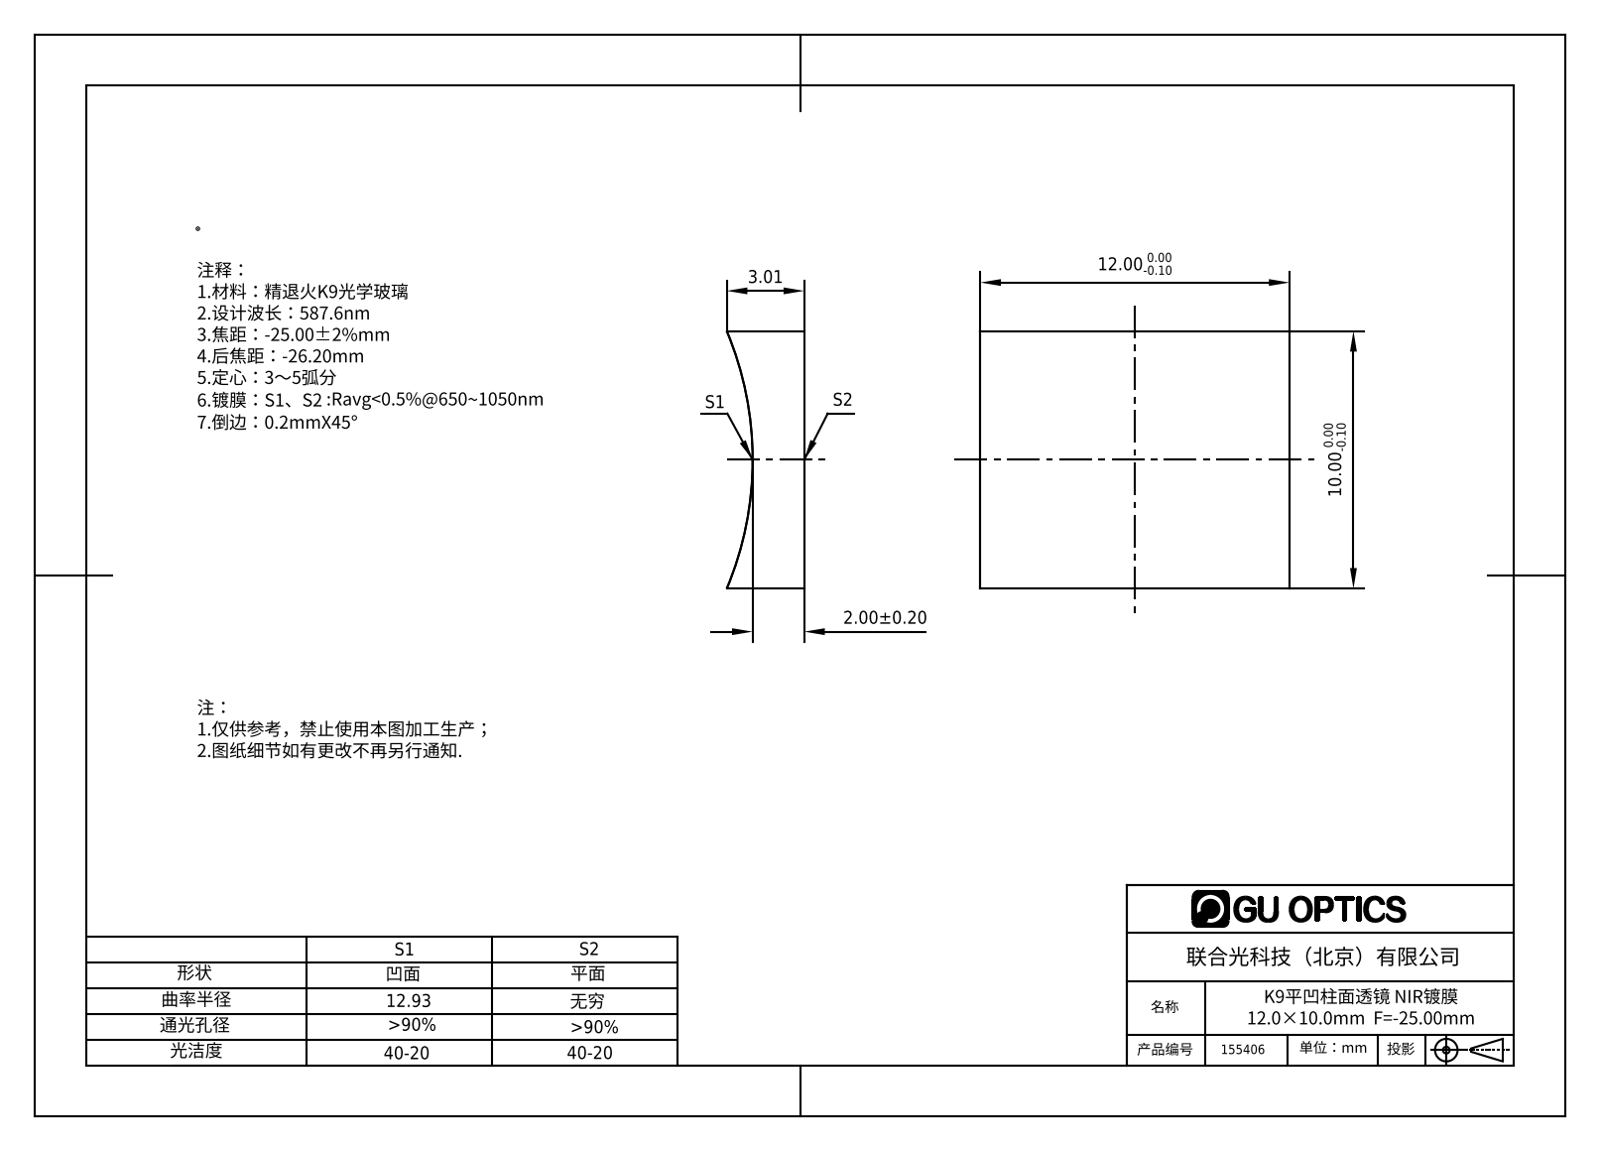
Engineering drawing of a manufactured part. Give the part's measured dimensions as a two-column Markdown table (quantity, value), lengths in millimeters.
| quantity | value |
| --- | --- |
| part name | 155340 |
| STEP written by | SolidWorks 2016 (AUTOMOTIVE_DESIGN) |
| units | millimeters |
| bodies | 1 solid, 6 faces (5 planar, 1 cylindrical, 0 other) |
| overall size | 12 × 10 × 3.01 |
| volume | 280 mm³ |
| surface area | 362 mm² |
| partial cylindrical surfaces (radius × count) | 12.93 × 1 |
| main face-to-face distances | 10, 12 |
